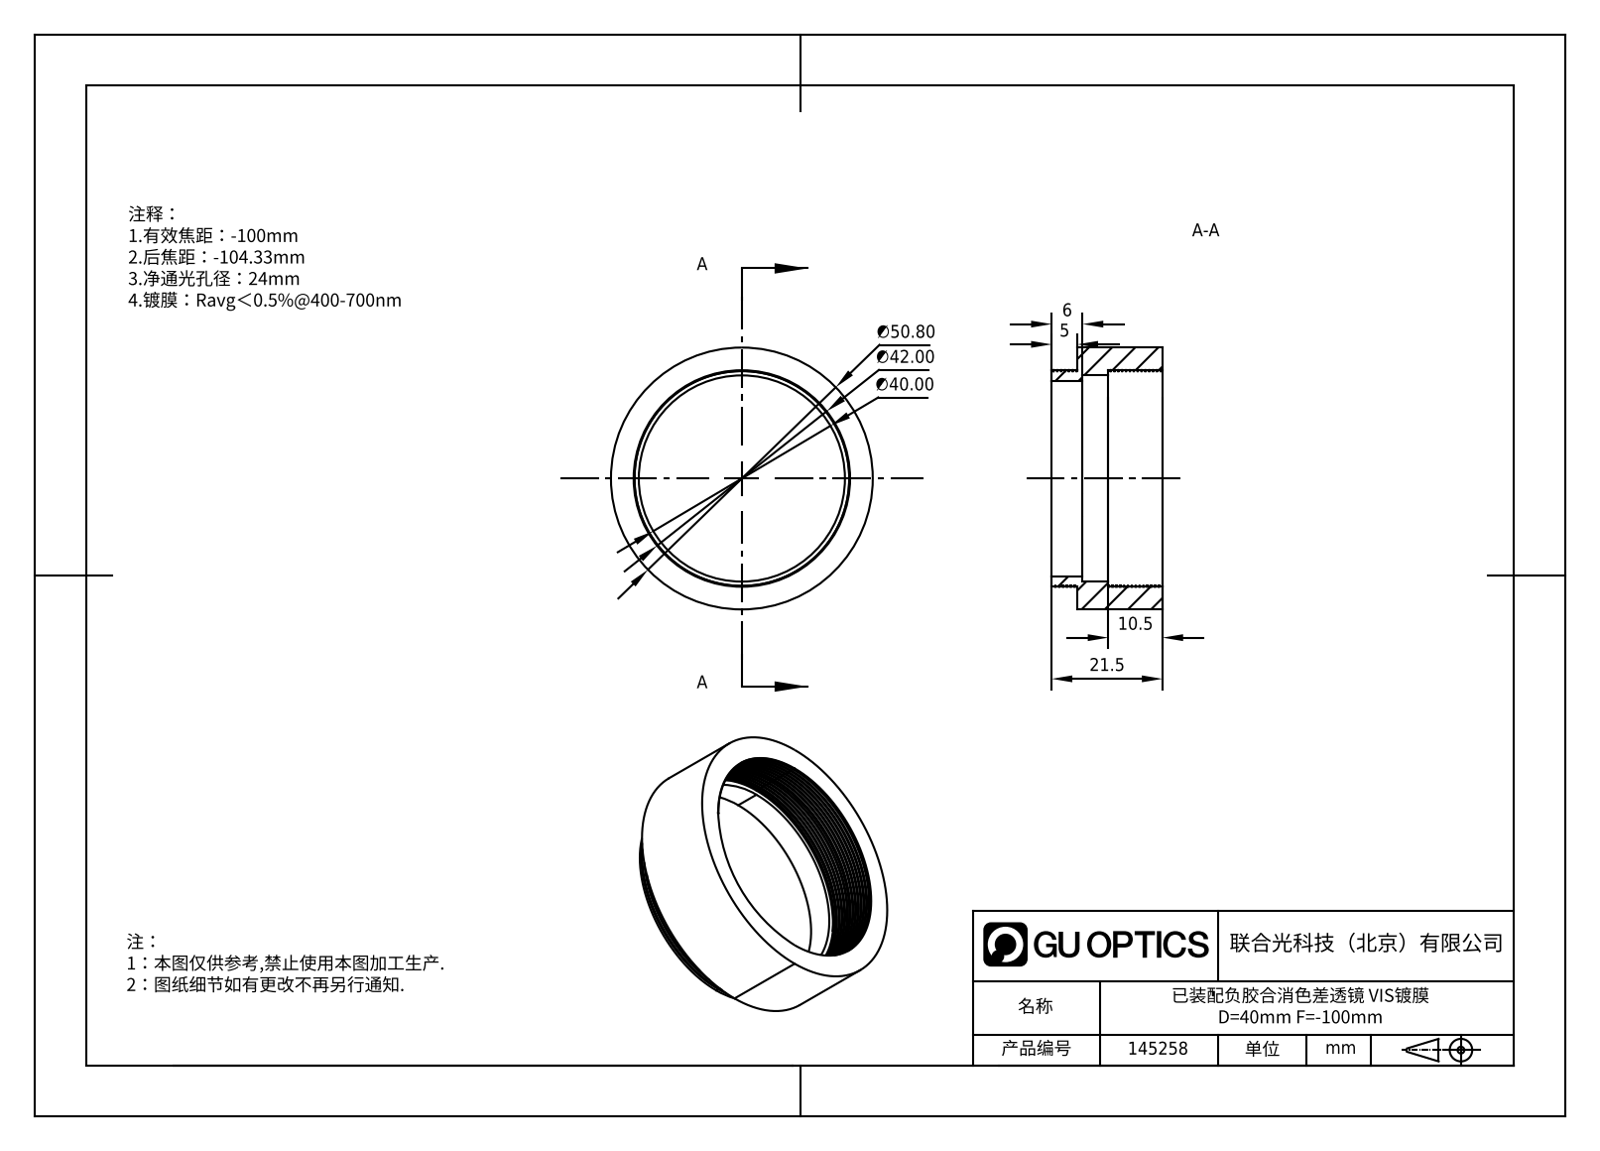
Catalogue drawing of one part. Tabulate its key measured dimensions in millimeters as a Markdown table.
| quantity | value |
| --- | --- |
| part name | APD-ML40-160-VIS-B |
| STEP written by | SolidWorks 2023 (CONFIG_CONTROL_DESIGN) |
| units | millimeters |
| bodies | 1 solid, 68 faces (9 planar, 52 cylindrical, 7 other) |
| overall size | 50.8 × 50.8 × 21.5 |
| volume | 12 774 mm³ |
| surface area | 10 612 mm² |
| round holes (diameter × count) | 38 × 1, 40 × 1, 42 × 1 |
| round bosses / shafts (diameter × count) | 50.8 × 1 |
| main face-to-face distances | 1, 1.01, 16.5, 15.5, 15.49, 5, 6, 6.01, 21.5, 11 |
